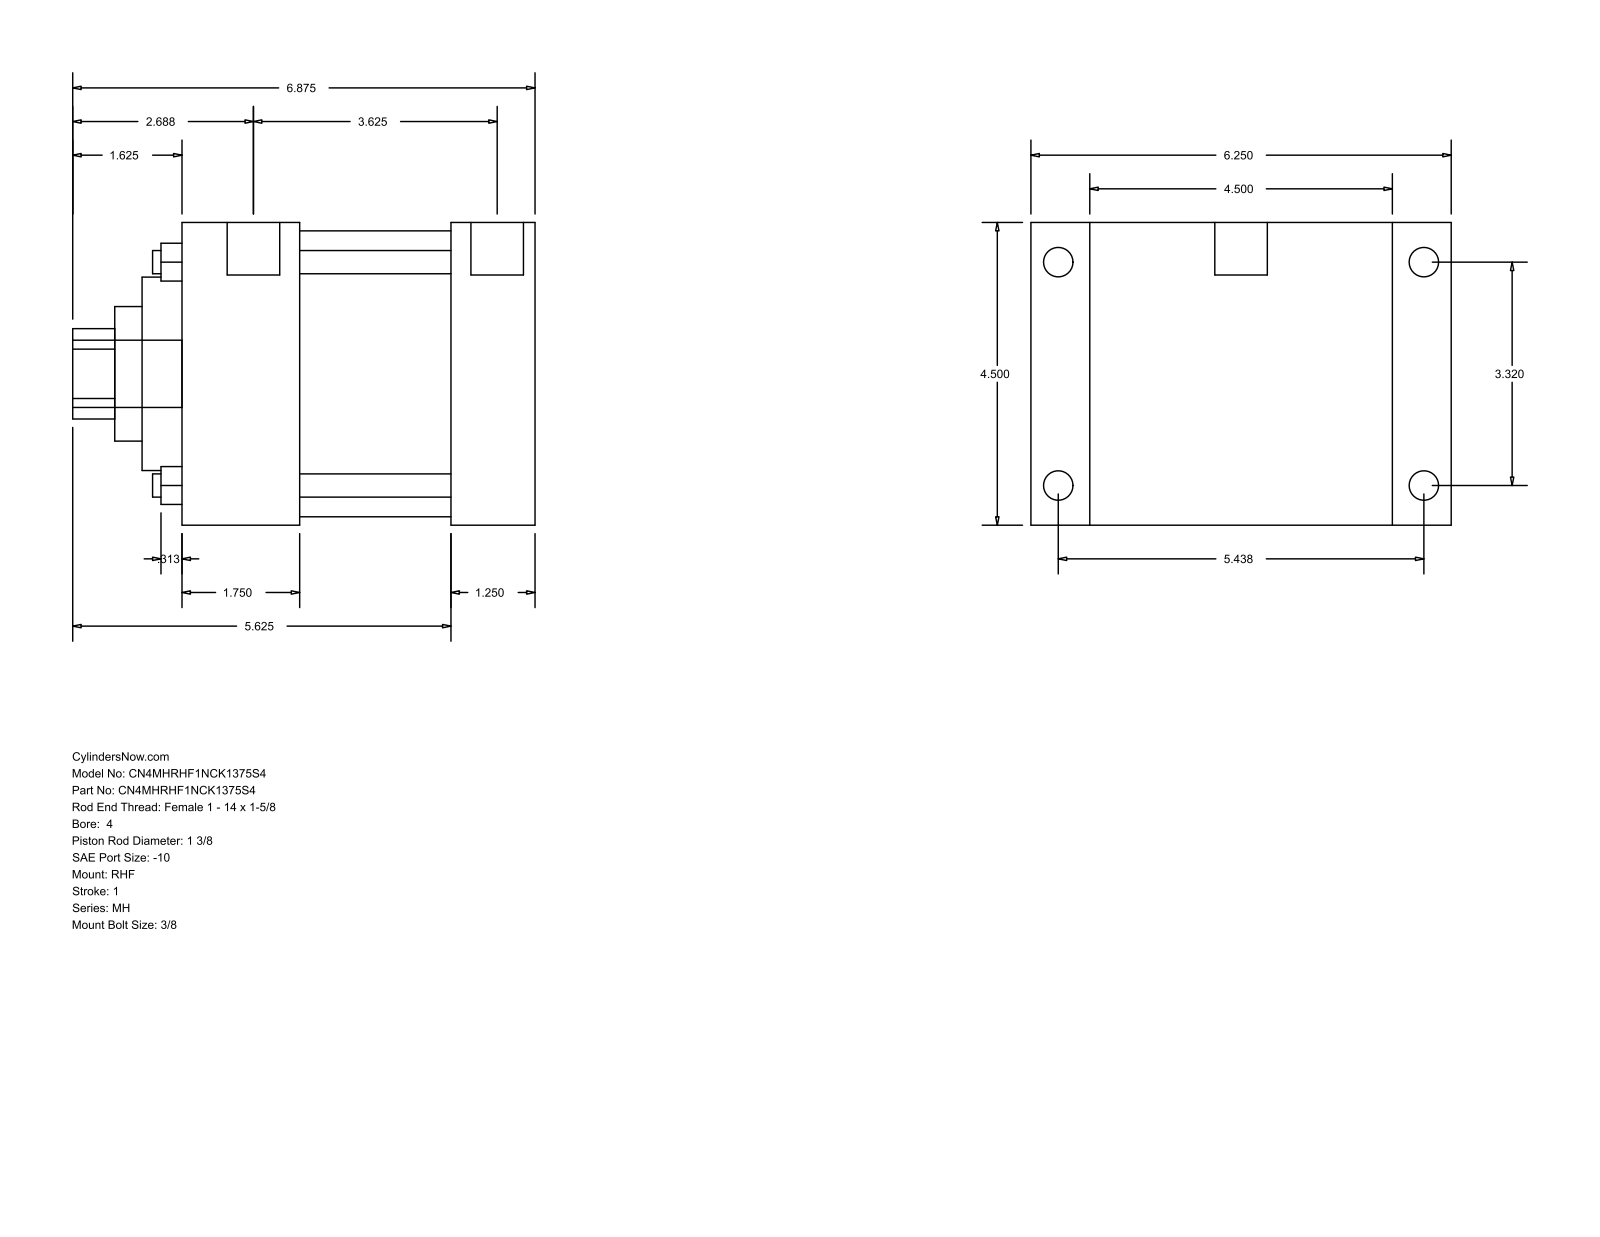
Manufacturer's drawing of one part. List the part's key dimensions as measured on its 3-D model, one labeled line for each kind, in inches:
Part name (STEP PRODUCT): MH_RHF__0400_1.375
STEP written by: GSSL Pune (CONFIG_CONTROL_DESIGN)
Units: inches
Bodies: 0 solids, 90 faces (61 planar, 29 cylindrical, 0 other)
Overall size (bounding box): 6.875 × 6.25 × 4.5
Round holes (diameter × count): ⌀0.345 ×4, ⌀1.375 ×1, ⌀2 ×1, ⌀2.875 ×1, ⌀4.25 ×1
Round bosses / shafts (diameter × count): ⌀0.438 ×4, ⌀0.344 ×4, ⌀0.781 ×2, ⌀1 ×1
Partial cylindrical surfaces — rounded edges, fillets, slot ends (radius × count): R0.672 ×1
Main face-to-face distances: 4.5, 5.25, 4, 1.25, 0.875, 5.375, 1.75, 2.25, 3.5, 6.25
Hole centre spacings: 2.347, 3.32, 4.695
